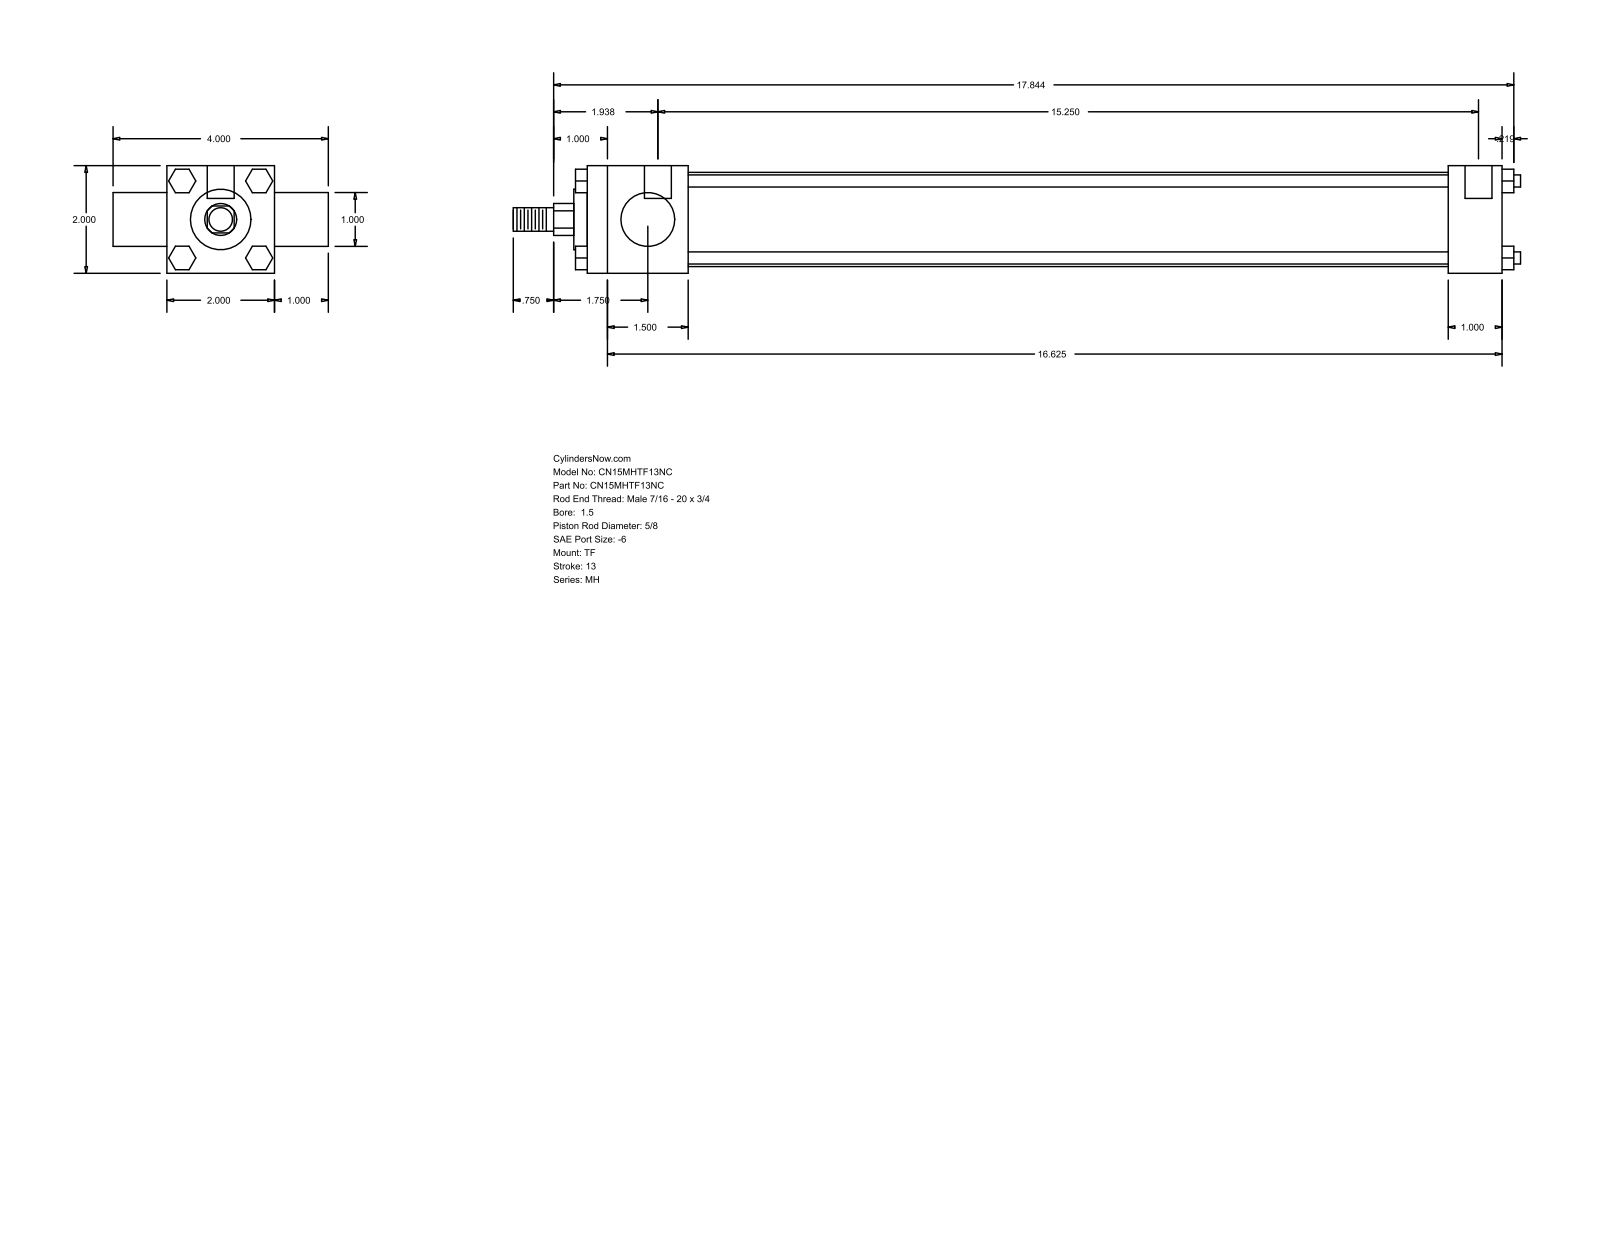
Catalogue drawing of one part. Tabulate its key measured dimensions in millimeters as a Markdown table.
| quantity | value |
| --- | --- |
| part name | MH_TF__0150_0.625 |
| STEP written by | GSSL Pune (CONFIG_CONTROL_DESIGN) |
| units | millimeters |
| bodies | 0 solids, 120 faces (92 planar, 28 cylindrical, 0 other) |
| overall size | 475.46 × 101.6 × 50.8 |
| round holes (diameter × count) | 5.56 × 3, 12.7 × 2 |
| round bosses / shafts (diameter × count) | 5.71 × 4, 44.45 × 1, 28.57 × 1, 25.4 × 1, 15.88 × 1, 11.11 × 1 |
| partial cylindrical surfaces (radius × count) | 7.54 × 1 |
| main face-to-face distances | 50.8, 431.8, 25.4, 76.2, 47.62, 384.18, 406.39, 358.77, 25.41, 11.11 |
| hole center spacings | 3.17, 387.35, 390.52 |
